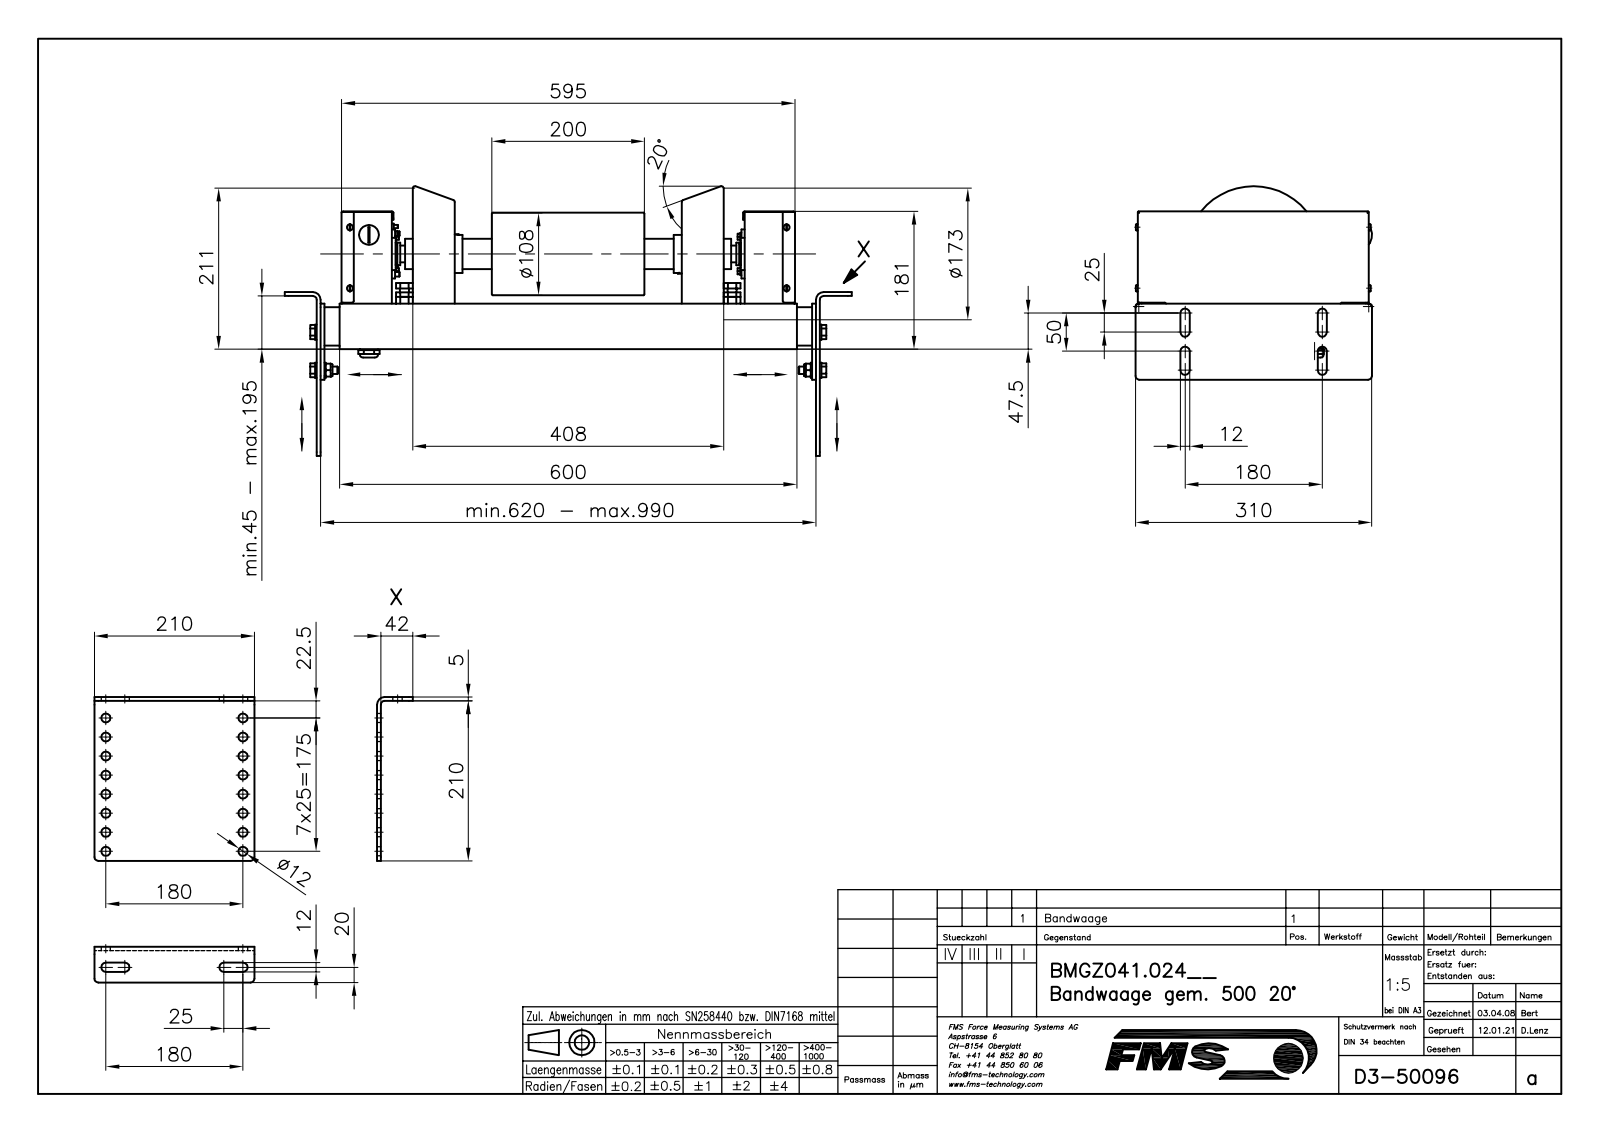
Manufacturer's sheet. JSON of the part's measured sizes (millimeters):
{"part_name": "B50096_STP; B50028; 6KT-SCHRAUBE_M12X30; ZYL_SCHR__M4X8 (+8 more)", "step_written_by": "Mechanical Desktop 2009 (CONFIG_CONTROL_DESIGN)", "units": "millimeters", "bodies": {"solids": 159, "faces": 2640, "planar": 1351, "cylindrical": 946, "other": 343}, "overall_size": [744, 353.93, 310.2], "volume_mm3": 6080000, "surface_area_mm2": 2480000, "round_holes": [[12, 17], [5, 6], [3.5, 4], [4.9, 4], [6.4, 4], [8.68, 4], [8.75, 4], [10, 4], [10.5, 4], [10.68, 4], [14.8, 4], [4.1, 3]], "round_bosses_or_shafts": [[12, 11], [8.2, 8], [4.2, 8], [20, 6], [10, 6], [5, 5], [16, 4], [11.1, 4]], "partial_cylinders_radius": [[2, 34], [1, 24], [4, 16], [5, 16], [6, 14], [3.5, 8], [2.25, 6], [0.5, 4]], "face_to_face_distances": [4, 5, 1, 3, 27.5, 650, 36, 270, 66, 65], "hole_center_spacings": [25, 181.73, 50, 186.82, 75, 195, 100, 180]}
